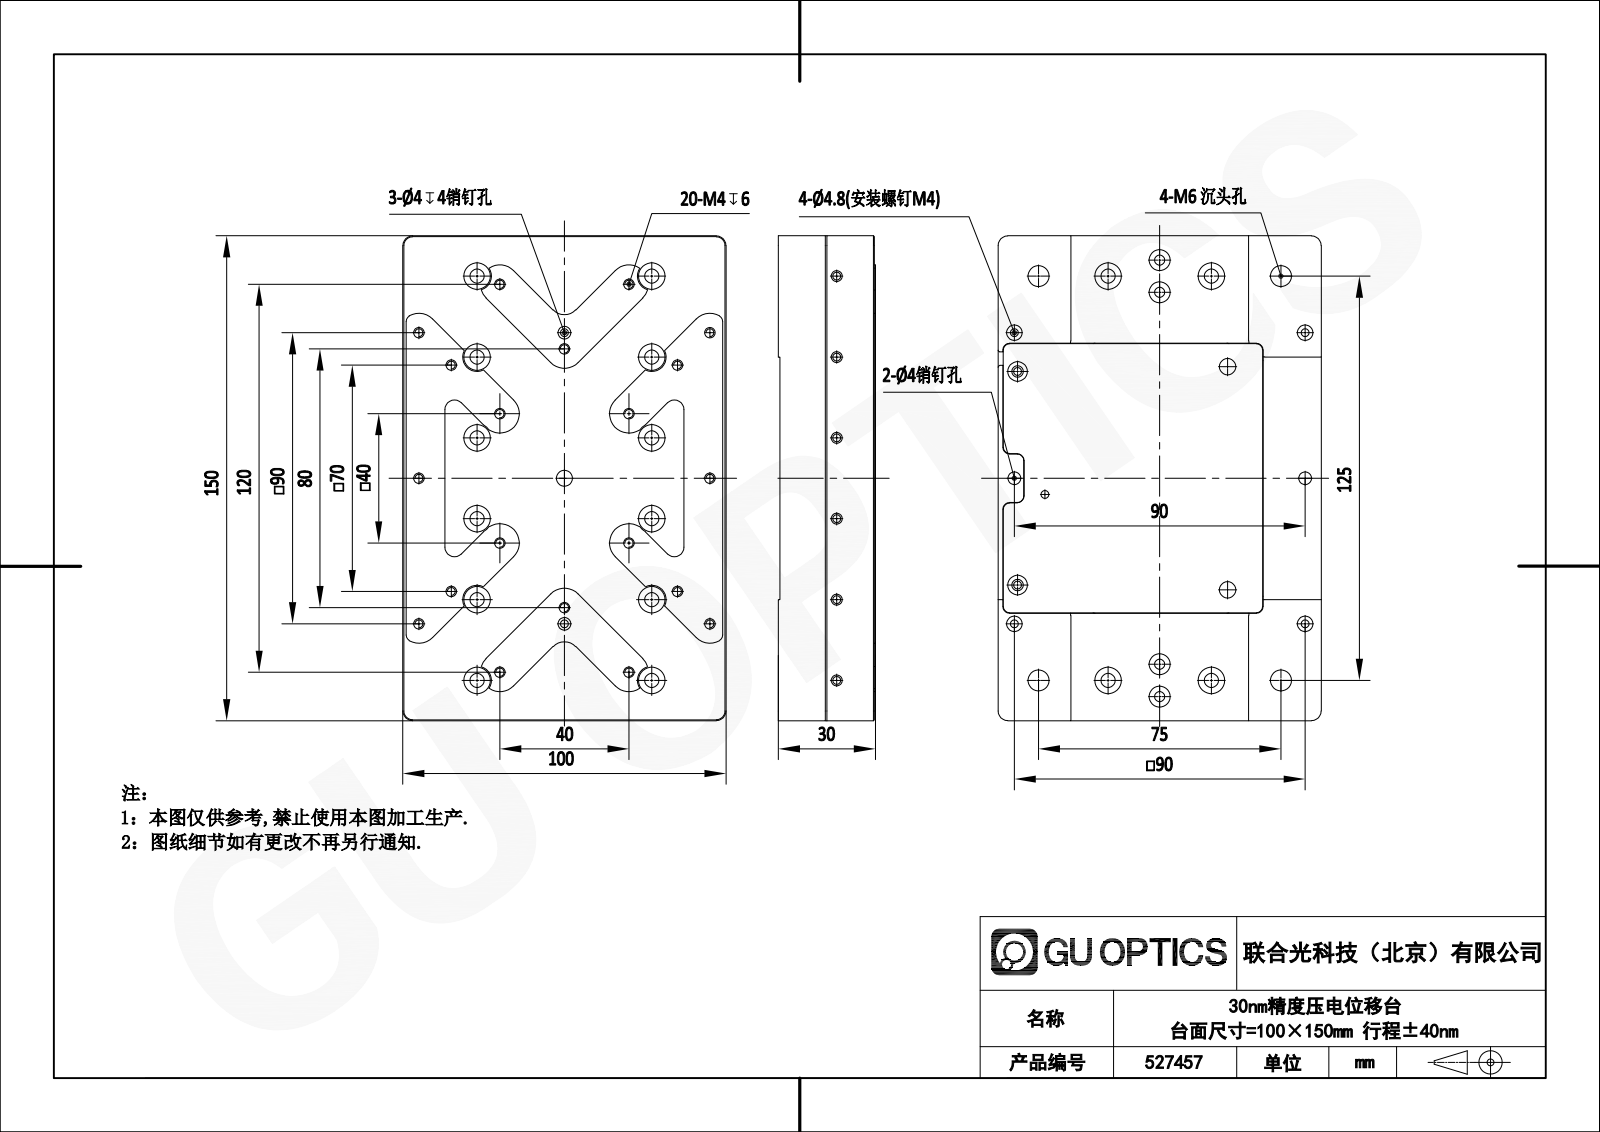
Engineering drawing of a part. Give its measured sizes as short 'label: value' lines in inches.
name: DG_LS3-1080-V2-JCEL; 527457ёьРВ4.17; HT_LS3-1080-V2-JCEL; JZ_LS3-1080-V2-JCEL
written by: SolidWorks 2020 (CONFIG_CONTROL_DESIGN)
unit: in
bodies: 3 solids, 723 faces (379 planar, 298 cylindrical, 46 other)
size: 5.906 × 3.937 × 1.181
volume: 23.56 in³; area: 174.8 in²
holes: 28× ⌀0.177, 21× ⌀0.098, 20× ⌀0.13, 20× ⌀0.325, 6× ⌀0.138, 4× ⌀0.126, 4× ⌀0.157, 4× ⌀0.189, 4× ⌀0.256, 4× ⌀0.26, 4× ⌀0.315, 4× ⌀0.441
rounds: 48× R0.098, 22× R0.079, 15× R0.118, 14× R0.236, 12× R0.177, 10× R0.059, 8× R0.157, 6× R0.075
face distances: 0.02, 0.354, 0.244, 0.335, 1.15, 0.598, 0.906, 0.551, 0.571, 0.591
hole spacings: 0.984, 1.969, 2.953, 1.599, 0.66, 1.489, 2.337, 4.921
